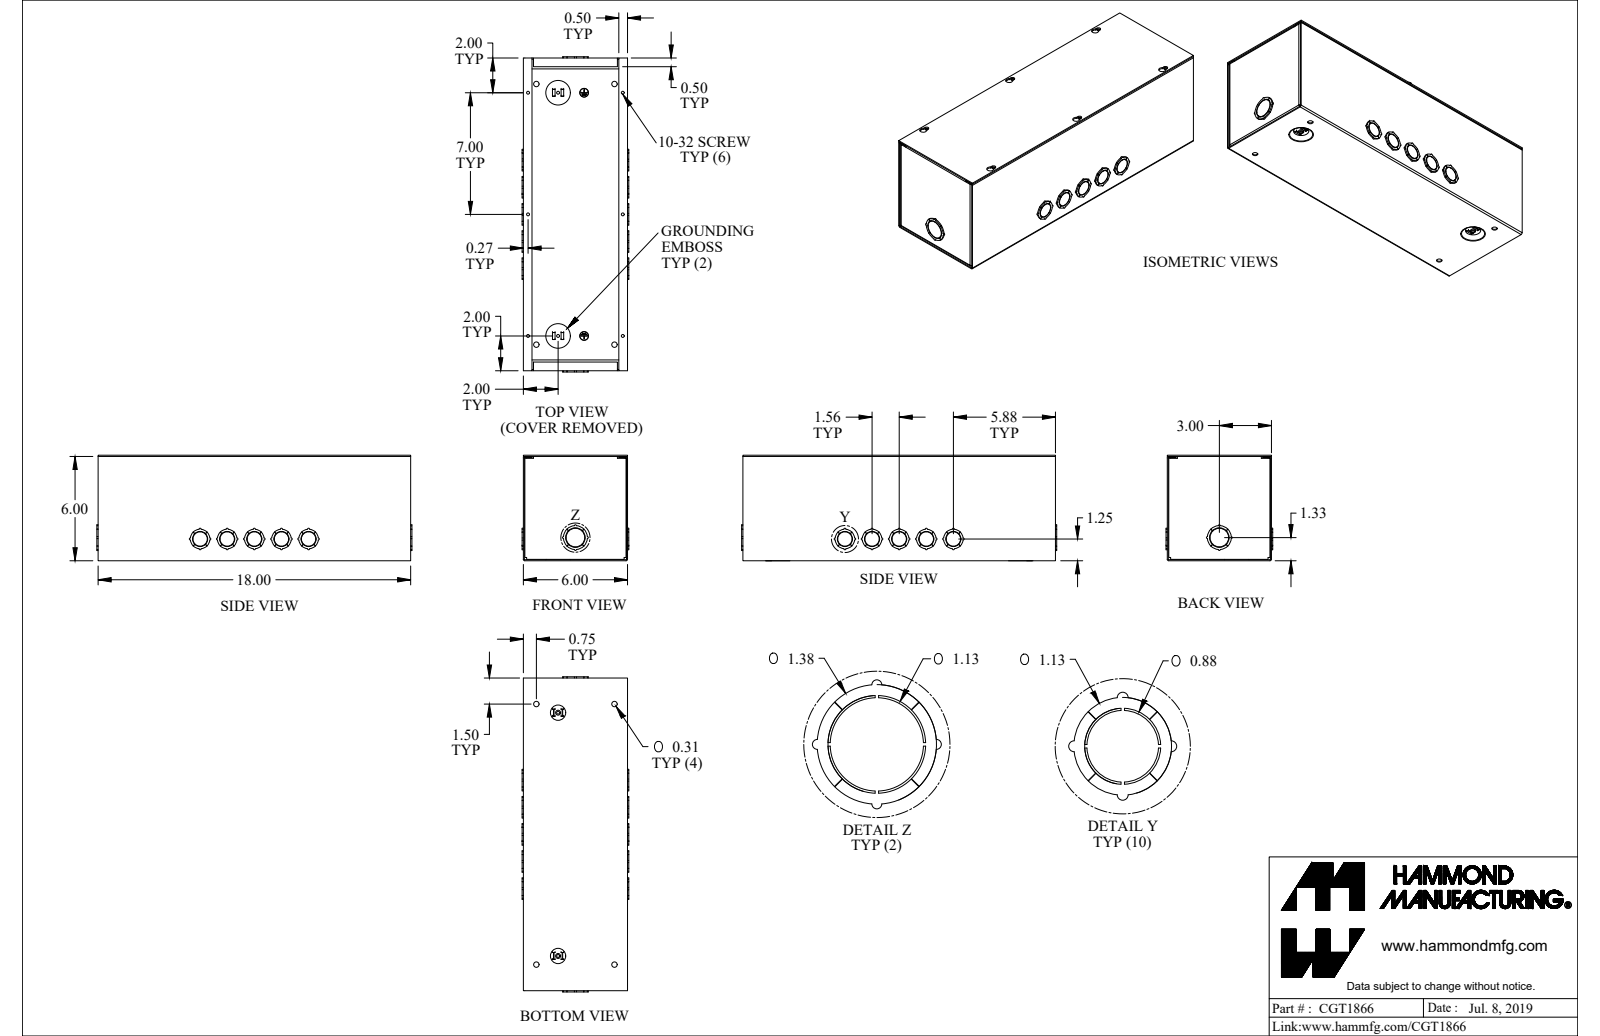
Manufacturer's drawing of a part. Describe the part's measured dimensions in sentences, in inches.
The part is named "CGT1866". Its 3-D file was written by "SolidWorks 2021 (AUTOMOTIVE_DESIGN)". It is 6 solids with 788 faces: 412 planar, 362 cylindrical and 14 other. Overall it measures 18.144 by 6.247 by 6.144 inches. Its volume is 34.34 cubic inches and its surface area 1 091 square inches. Round holes: 8 of diameter 0.17, 5 of diameter 0.875, 4 of diameter 0.312, 2 of diameter 0.5, 1 of diameter 1.125. Round bosses or shafts: 5 of diameter 1.125, 5 of diameter 0.825, 2 of diameter 0.492, 2 of diameter 0.284, 2 of diameter 0.19, 1 of diameter 1.375, 1 of diameter 1.075, 1 of diameter 0.375. Partial cylindrical surfaces (rounded edges, fillets, slot ends): 20 of radius 0.062, 8 of radius 0.036, 8 of radius 0.057, 8 of radius 0.108, 6 of radius 0.125, 6 of radius 0.203, 4 of radius 0.029, 4 of radius 0.057. The main face-to-face distances are 0.057, 5.943, 0.072, 6, 5.886, 6.072, 6.015, 17.928, 18, 17.856. The hole center spacings are 0.693, 5.005, 7, 7.515, 8.878, 9.003, 14, 14.508.
